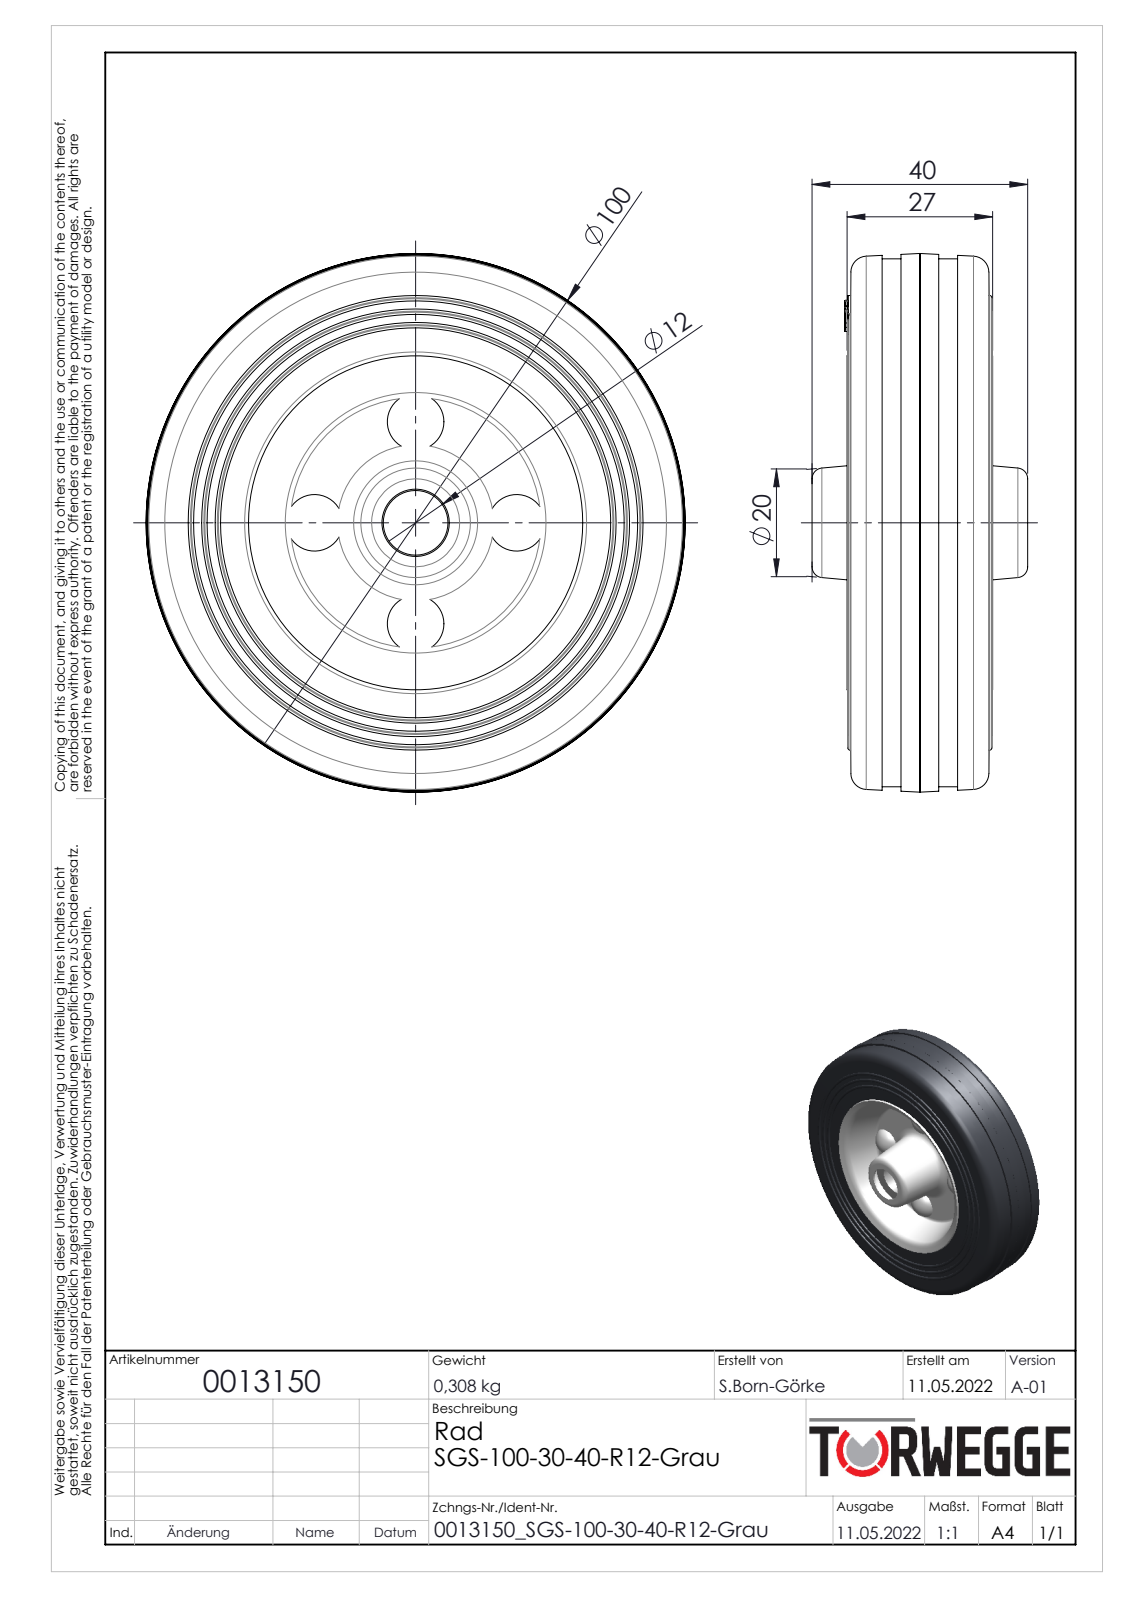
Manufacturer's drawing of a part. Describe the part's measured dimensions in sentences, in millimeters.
The part is named "0013150". Its 3-D file was written by "SolidWorks 2020 (AUTOMOTIVE_DESIGN)". It is 0 solids with 269 faces: 48 planar, 47 cylindrical and 174 other. Overall it measures 100 by 100 by 40 millimeters. Round holes: 1 of diameter 12, 1 of diameter 12.5, 1 of diameter 72.38, 1 of diameter 77.38, 1 of diameter 82.38. Round bosses or shafts: 1 of diameter 98, 1 of diameter 84.38, 1 of diameter 79.38, 1 of diameter 74.38. Partial cylindrical surfaces (rounded edges, fillets, slot ends): 2 of radius 3. The main face-to-face distances are 1.4, 2.8, 4.2, 11.5, 14.3, 15.7, 18.5, 8, 22, 3.5.
